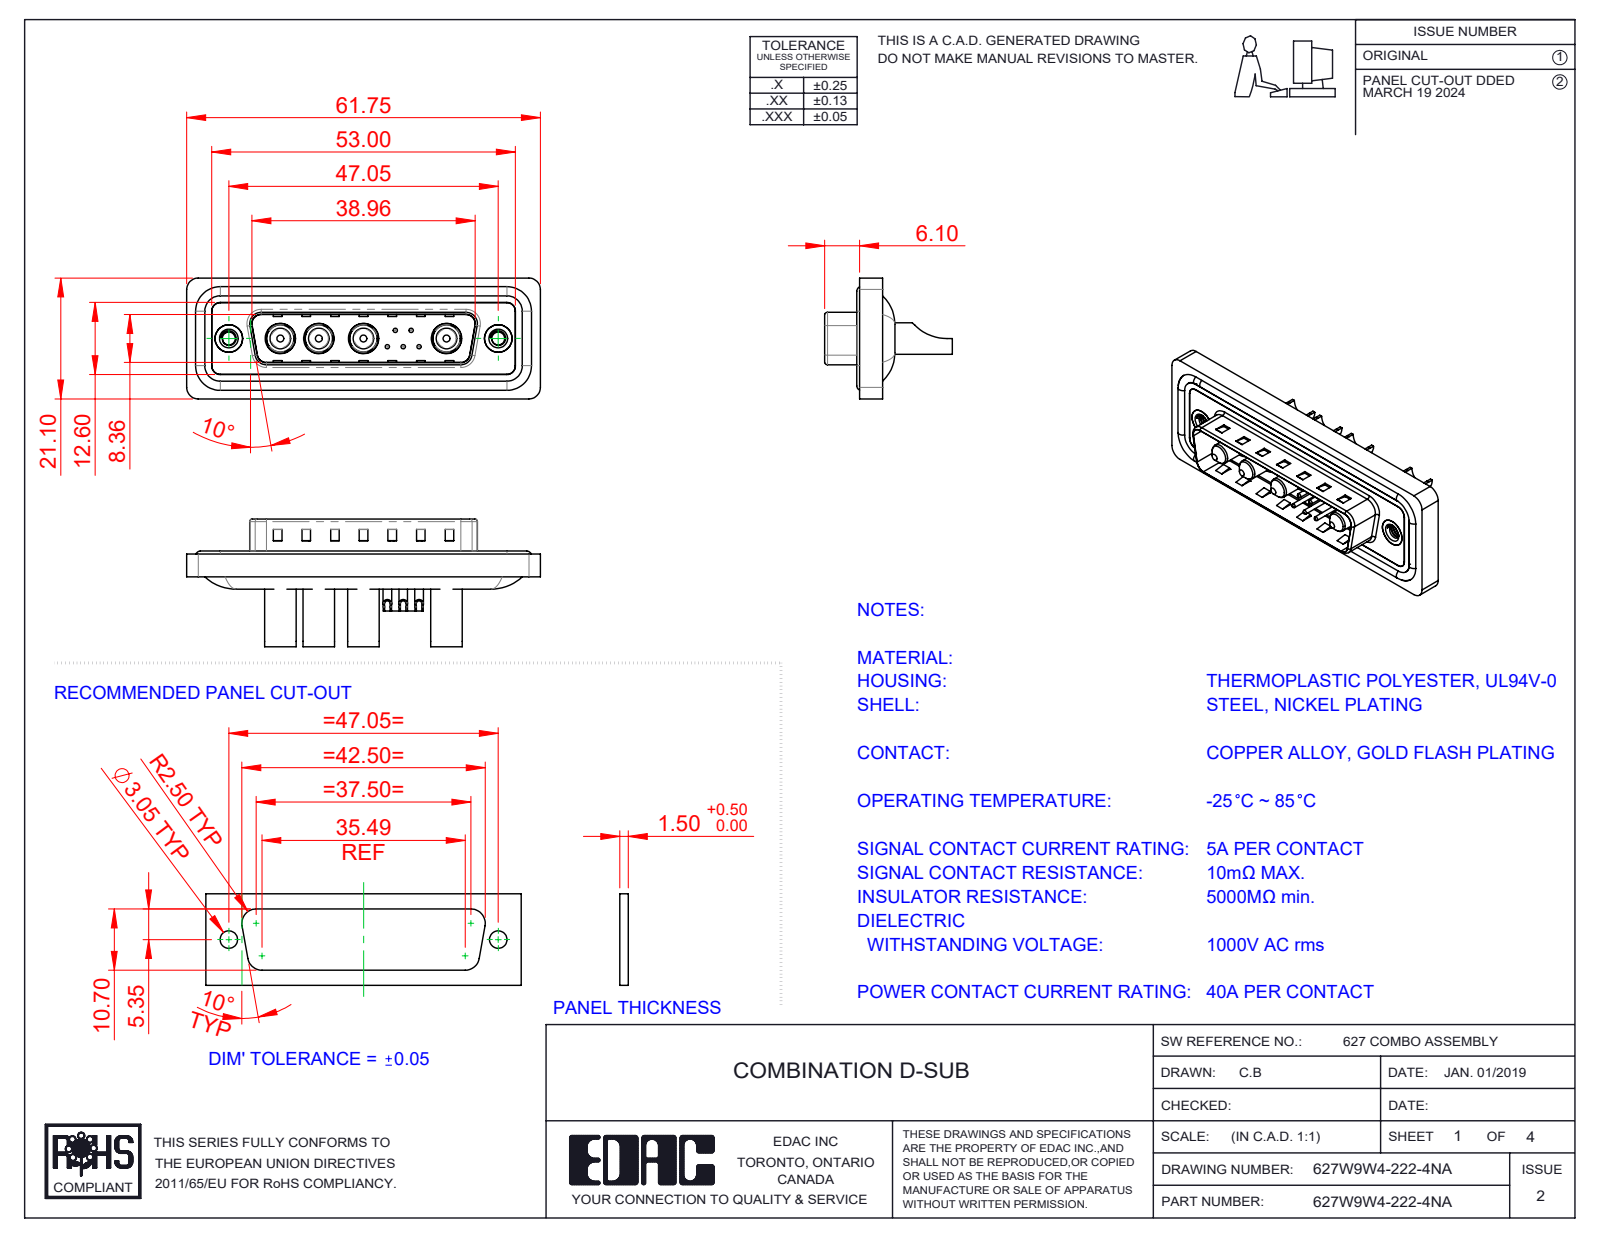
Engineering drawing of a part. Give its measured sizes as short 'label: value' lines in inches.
name: Power Pin_40A SC; 627W9W4-222-4NA; 627Combo Contact Row 2_22; 627Combo Housing_9W4 (+5 more)
written by: SolidWorks 2023 (CONFIG_CONTROL_DESIGN)
unit: in
bodies: 20 solids, 838 faces (302 planar, 350 cylindrical, 186 other)
size: 2.431 × 0.878 × 0.831
volume: 0.462 in³; area: 19.27 in²
holes: 5× ⌀0.03, 5× ⌀0.039, 5× ⌀0.063, 5× ⌀0.079, 4× ⌀0.181, 4× ⌀0.191, 4× ⌀0.209, 2× ⌀0.089, 2× ⌀0.157, 2× ⌀0.189, 2× ⌀0.197
bosses: 5× ⌀0.059, 4× ⌀0.217, 4× ⌀0.205, 4× ⌀0.187, 4× ⌀0.148, 4× ⌀0.142, 4× ⌀0.063, 2× ⌀0.193
rounds: 22× R0.059, 18× R0.079, 8× R0.02, 8× R0.063, 6× R0.039, 4× R0.01, 4× R0.024, 4× R0.026
face distances: 0.016, 0.043, 0.059, 0.02, 0.063, 0.122, 0.114, 0.032, 0.377, 0.222
hole spacings: 0.124, 0.109, 0.198, 0.571, 0.109, 0.173, 0.174, 0.197
